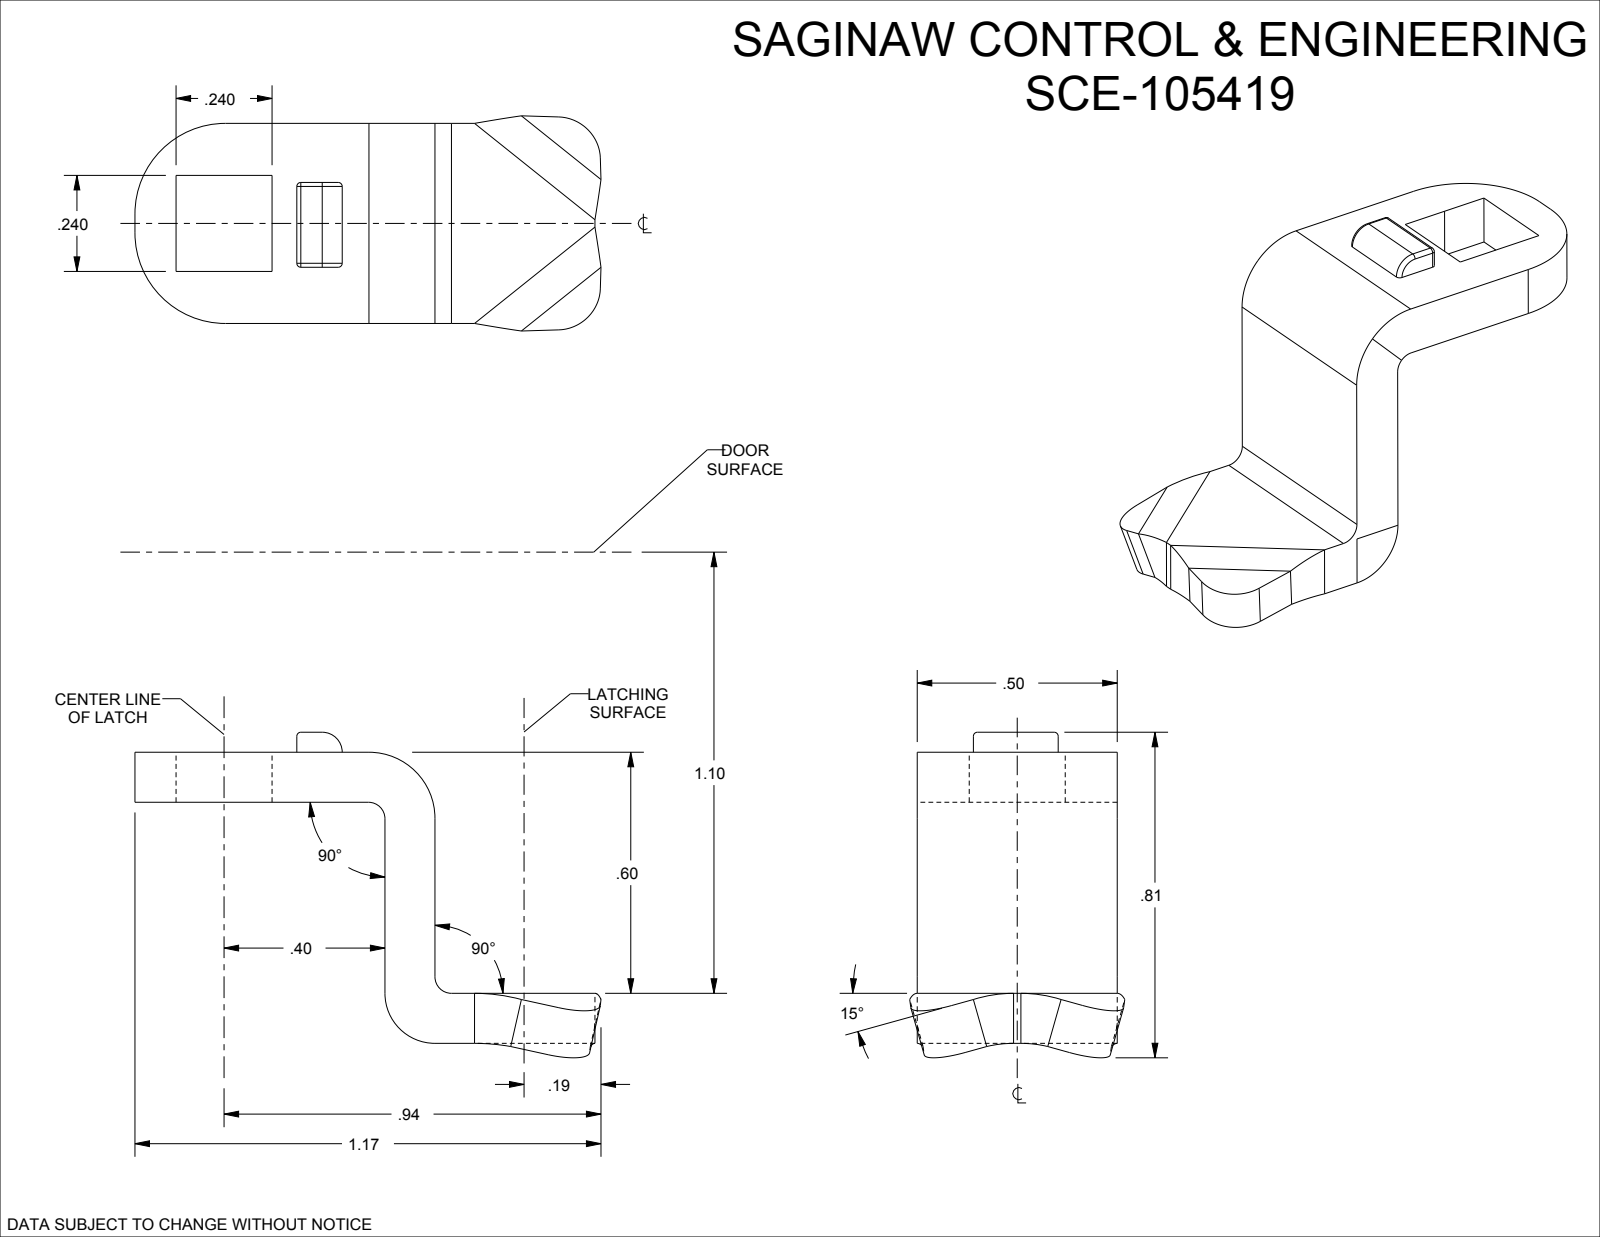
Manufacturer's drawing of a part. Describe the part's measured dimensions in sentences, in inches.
The part is named "SCE-105419". Its 3-D file was written by "SolidWorks 2019 (AUTOMOTIVE_DESIGN)". It is 1 solid with 63 faces: 37 planar, 18 cylindrical and 8 other. Overall it measures 1.165 by 0.814 by 0.538 inches. Its volume is 0.094 cubic inches and its surface area 2.218 square inches. Partial cylindrical surfaces (rounded edges, fillets, slot ends): 5 of radius 0.01, 2 of radius 0.041, 2 of radius 0.103, 2 of radius 0.132, 2 of radius 0.226, 2 of radius 0.257, 1 of radius 0.05, 1 of radius 0.125. The main face-to-face distances are 0.125, 0.5, 0.728, 0.603, 0.125, 0.602, 0.478, 0.24, 0.13, 0.37.
